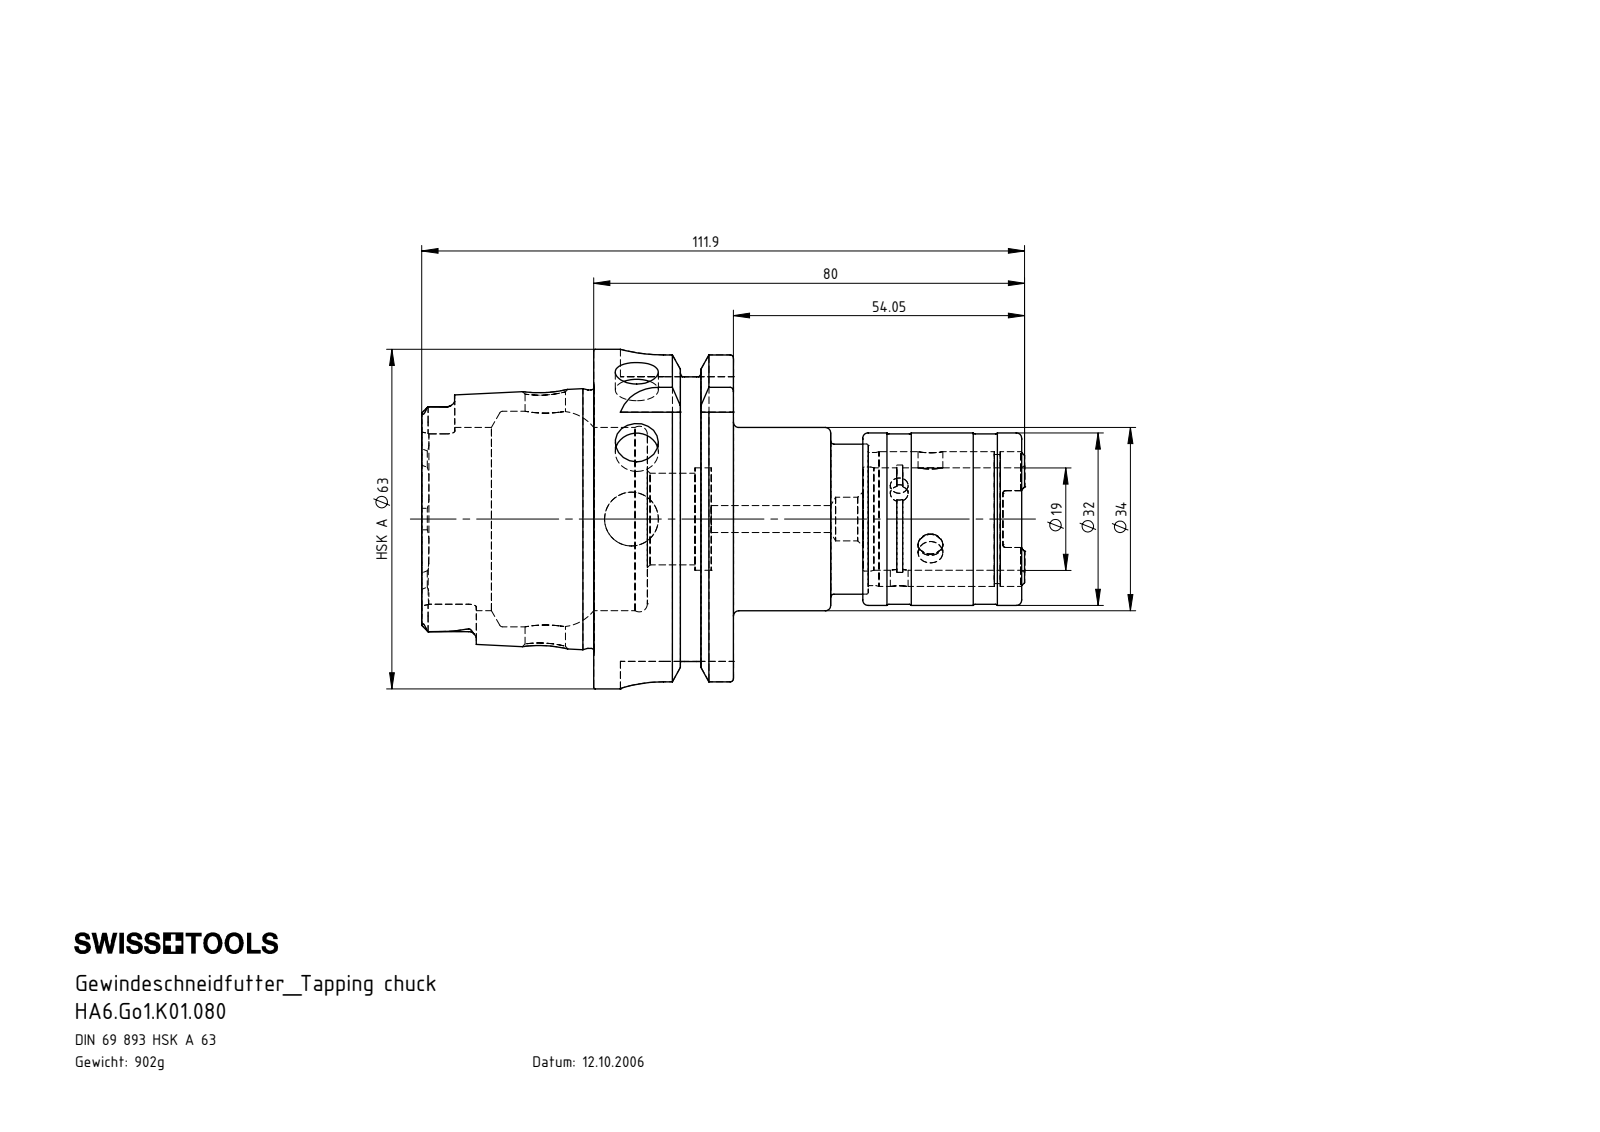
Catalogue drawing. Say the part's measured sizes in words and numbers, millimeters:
The part is named "HA6.Go1.K01.080; Einbausatz Go1_gespannt; Kugel Go1; Hülse Go1 (+6 more)". Its 3-D file was written by "SolidWorks 2011 (AUTOMOTIVE_DESIGN)". It is 10 solids with 391 faces: 90 planar, 121 cylindrical and 180 other. Overall it measures 111.9 by 63 by 63 millimeters. Its volume is 114 861 cubic millimeters and its surface area 39 115 square millimeters. Round holes: 3 of diameter 3.3, 3 of diameter 4.6, 3 of diameter 8, 1 of diameter 2, 1 of diameter 5, 1 of diameter 7.5, 1 of diameter 8.1, 1 of diameter 10, 1 of diameter 17, 1 of diameter 19, 1 of diameter 19.3, 1 of diameter 20.05. Round bosses or shafts: 1 of diameter 63, 1 of diameter 54.95, 1 of diameter 47.94, 1 of diameter 32, 1 of diameter 31.6, 1 of diameter 27.85, 1 of diameter 25, 1 of diameter 24.7. Partial cylindrical surfaces (rounded edges, fillets, slot ends): 6 of radius 1.4, 4 of radius 2.88, 4 of radius 8, 3 of radius 2.15, 2 of radius 0.5. The main face-to-face distances are 25.95, 16, 9.95, 31.9, 41.85, 57.85, 21.8, 52.8, 11.85, 53.7. The hole center spacings are 5.8, 65.7, 71.5.
